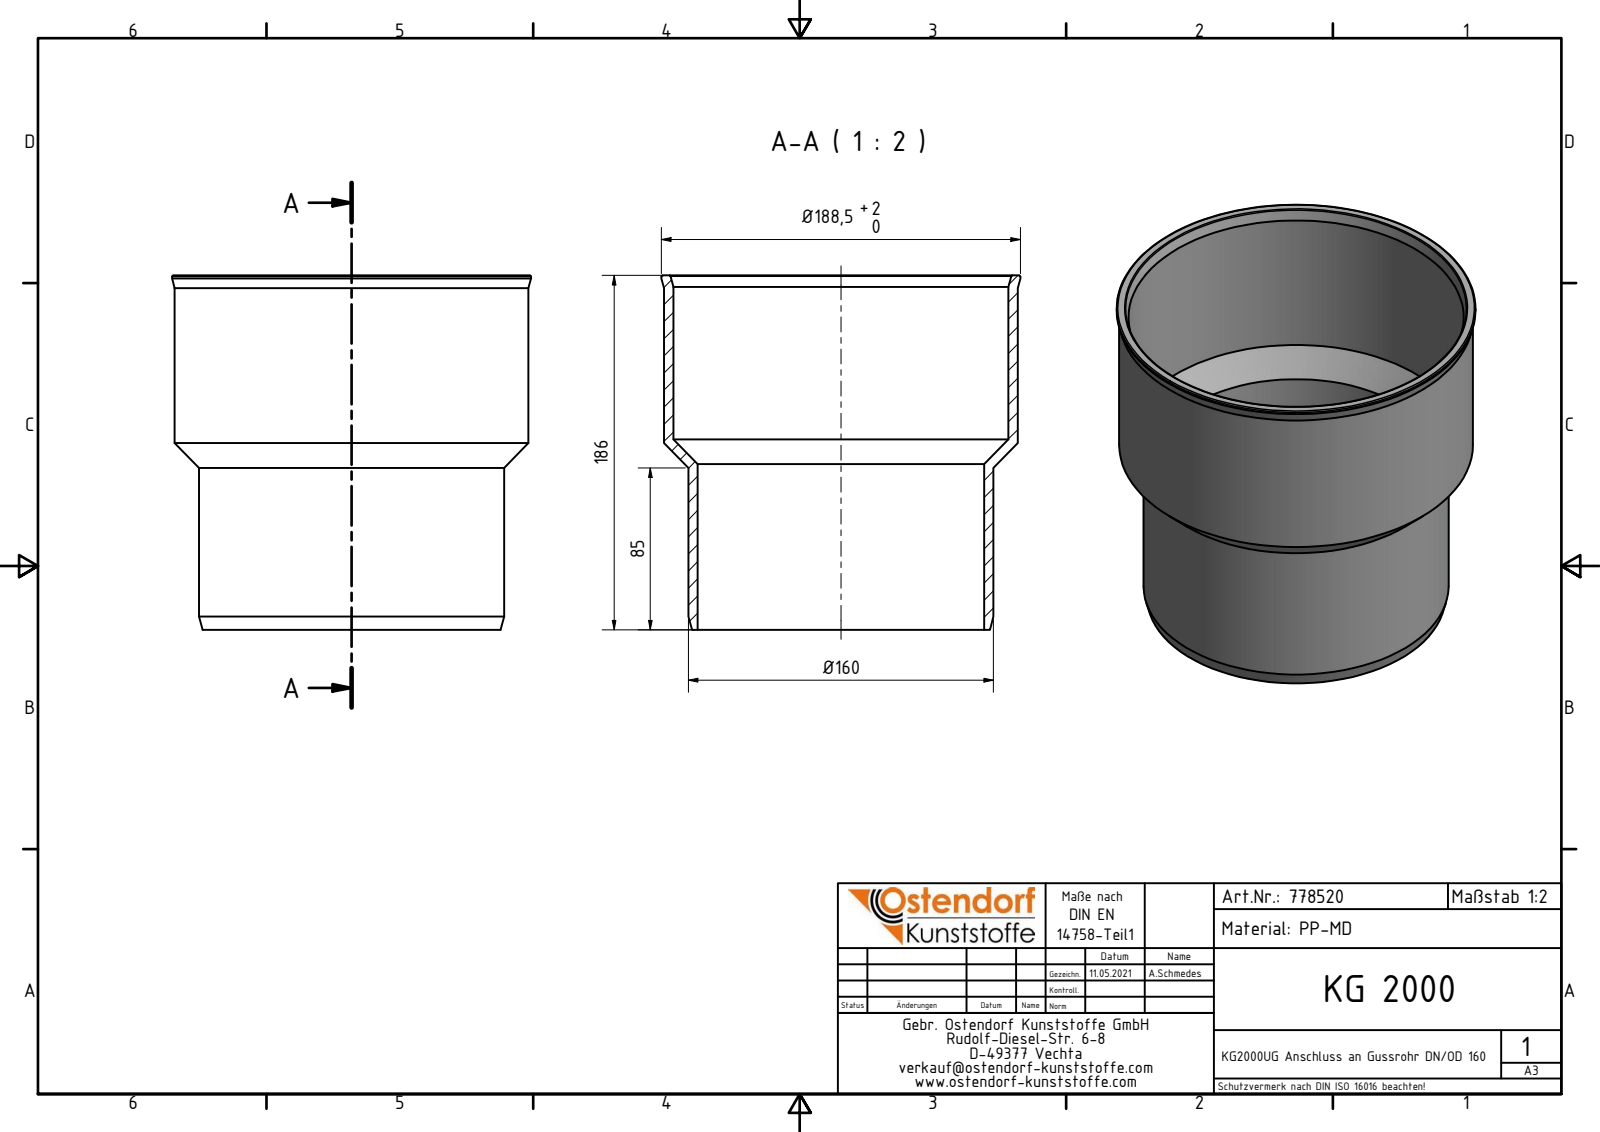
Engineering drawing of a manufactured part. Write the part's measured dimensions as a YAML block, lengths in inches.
part_name: "778520 KG2000UG Anschluss an Gussrohr DN_OD 160"
step_written_by: "Autodesk Inventor 2020 (AUTOMOTIVE_DESIGN)"
units: inches
bodies: {solids: 1, faces: 14, planar: 2, cylindrical: 5, other: 7}
overall_size: [7.421, 7.421, 7.323]
volume: 30.04
surface_area: 319.9
round_holes:
  - {diameter: 5.921, count: 1}
  - {diameter: 6.929, count: 1}
round_bosses_or_shafts:
  - {diameter: 7.421, count: 1}
  - {diameter: 7.315, count: 1}
  - {diameter: 6.307, count: 1}
face_to_face_distances: [7.323]
